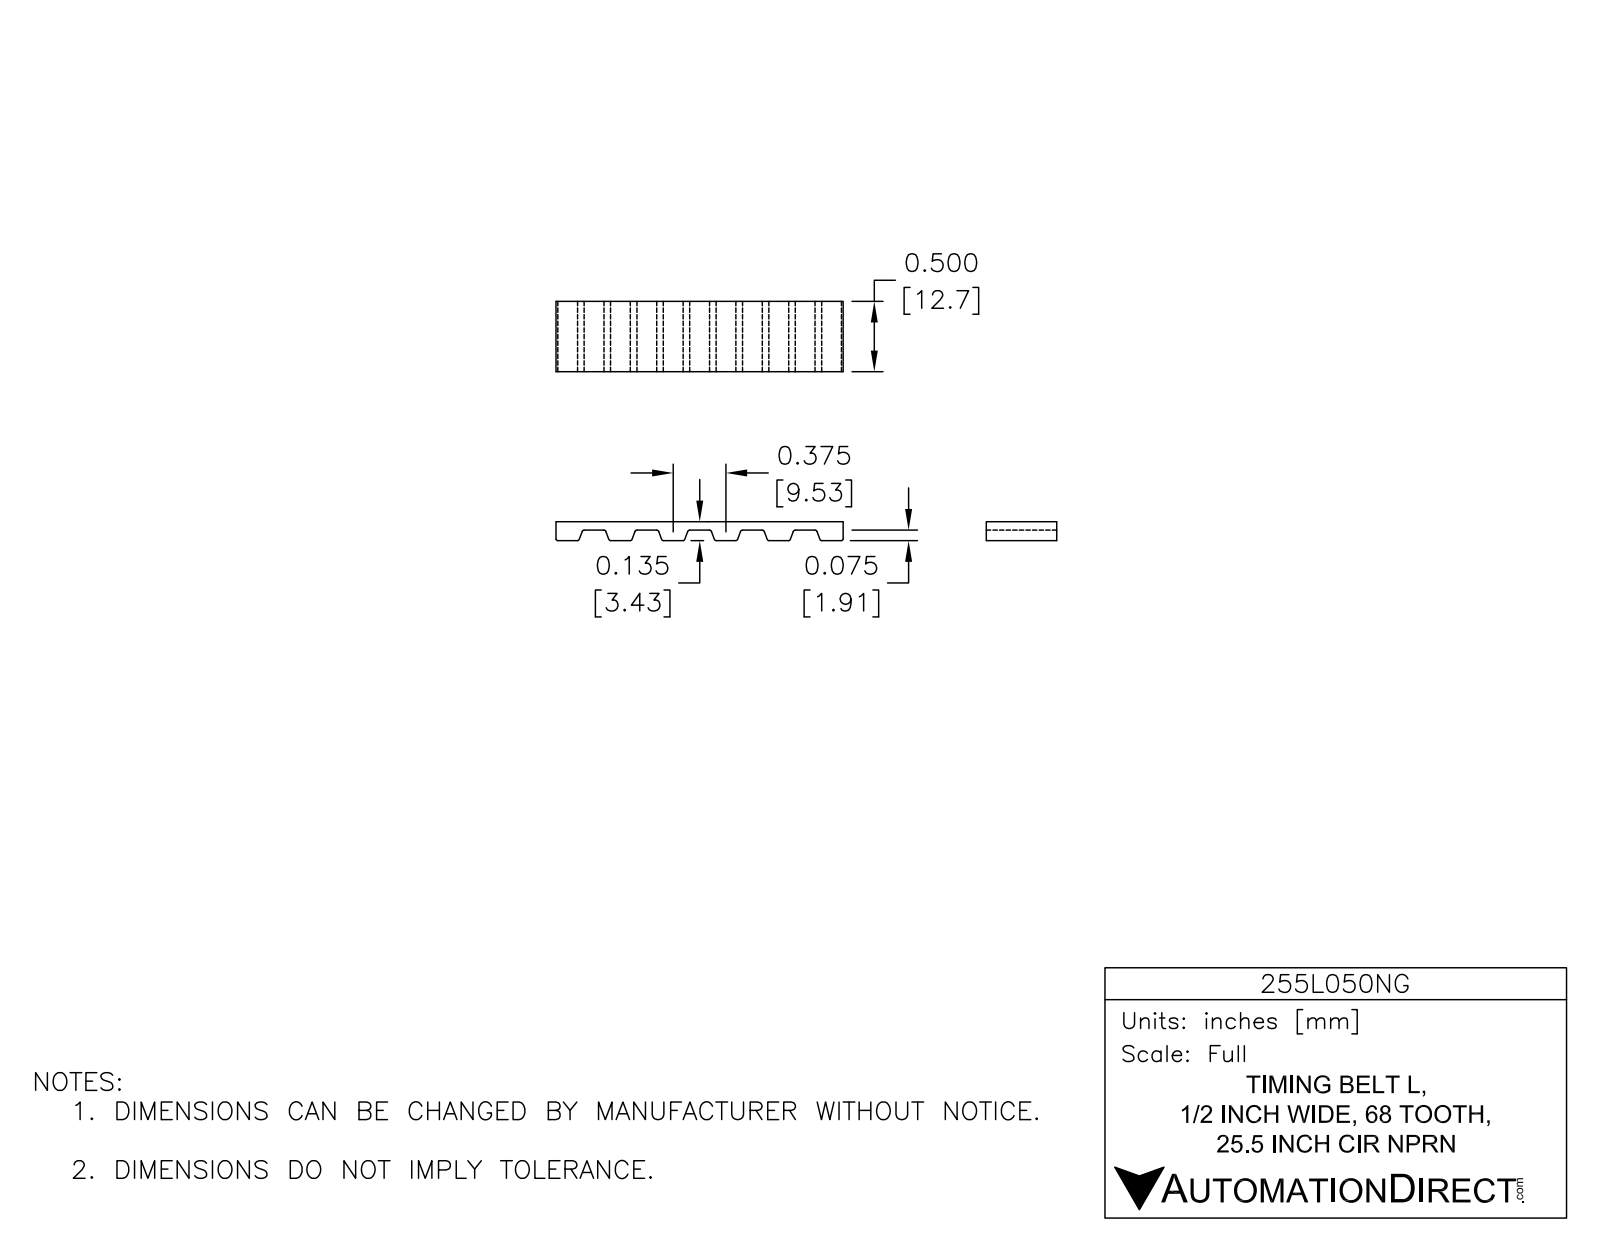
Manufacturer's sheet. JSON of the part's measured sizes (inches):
{"part_name": "255L050NG", "step_written_by": "SolidWorks 2014 (AUTOMOTIVE_DESIGN)", "units": "inches", "bodies": {"solids": 1, "faces": 559, "planar": 249, "cylindrical": 310, "other": 0}, "overall_size": [11.038, 3, 1], "volume_in3": 2.301, "surface_area_in2": 61.26, "partial_cylinders_radius": [[0.02, 268], [1.435, 2], [1.5, 2]], "face_to_face_distances": [0.065, 2.935, 3, 2.87, 0.14, 2.86, 0.075, 2.795, 1, 2.72]}
